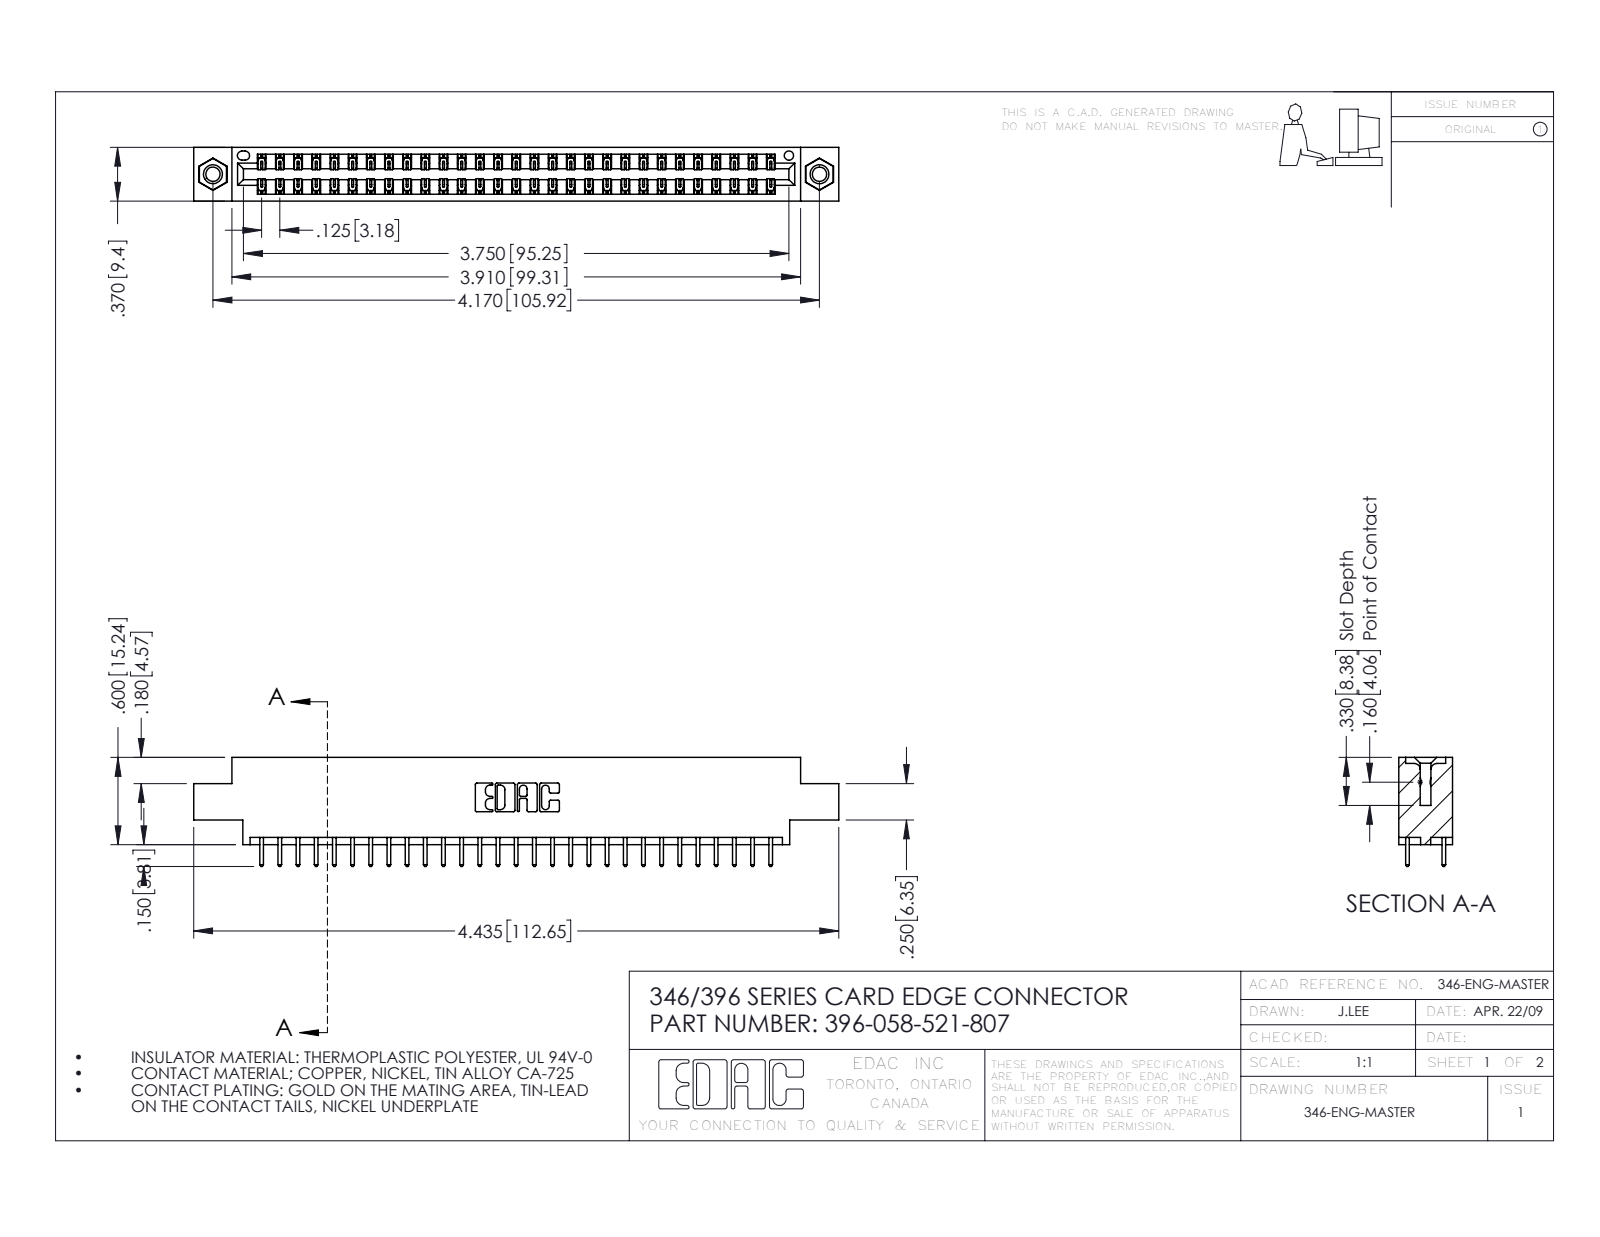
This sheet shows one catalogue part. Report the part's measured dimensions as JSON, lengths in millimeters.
{"part_name": "346 Part_0.170 Offset - 0.156 Dia-TI; 345-292-001_345-293-121; 396-058-521-807; 345-250-001_345-250-005-103", "step_written_by": "SolidWorks 2016 (CONFIG_CONTROL_DESIGN)", "units": "millimeters", "bodies": {"solids": 61, "faces": 3202, "planar": 2142, "cylindrical": 1044, "other": 16}, "overall_size": [112.6, 19.1, 9.4], "volume_mm3": 10700, "surface_area_mm2": 14550, "round_holes": [[2.5, 2], [3.2, 2], [4, 2], [1.6, 1]], "round_bosses_or_shafts": [[3.9, 2]], "partial_cylinders_radius": [[0.2, 87], [0.3, 58], [0.3, 22], [0.2, 6], [0.8, 6], [0.7, 3], [0.4, 2], [0.6, 2]], "face_to_face_distances": [1.2, 8.2, 9.4, 6.4, 1.8, 7.6, 0.6, 7, 5.6, 3.8], "hole_center_spacings": [6.2, 100.6, 105.9]}
